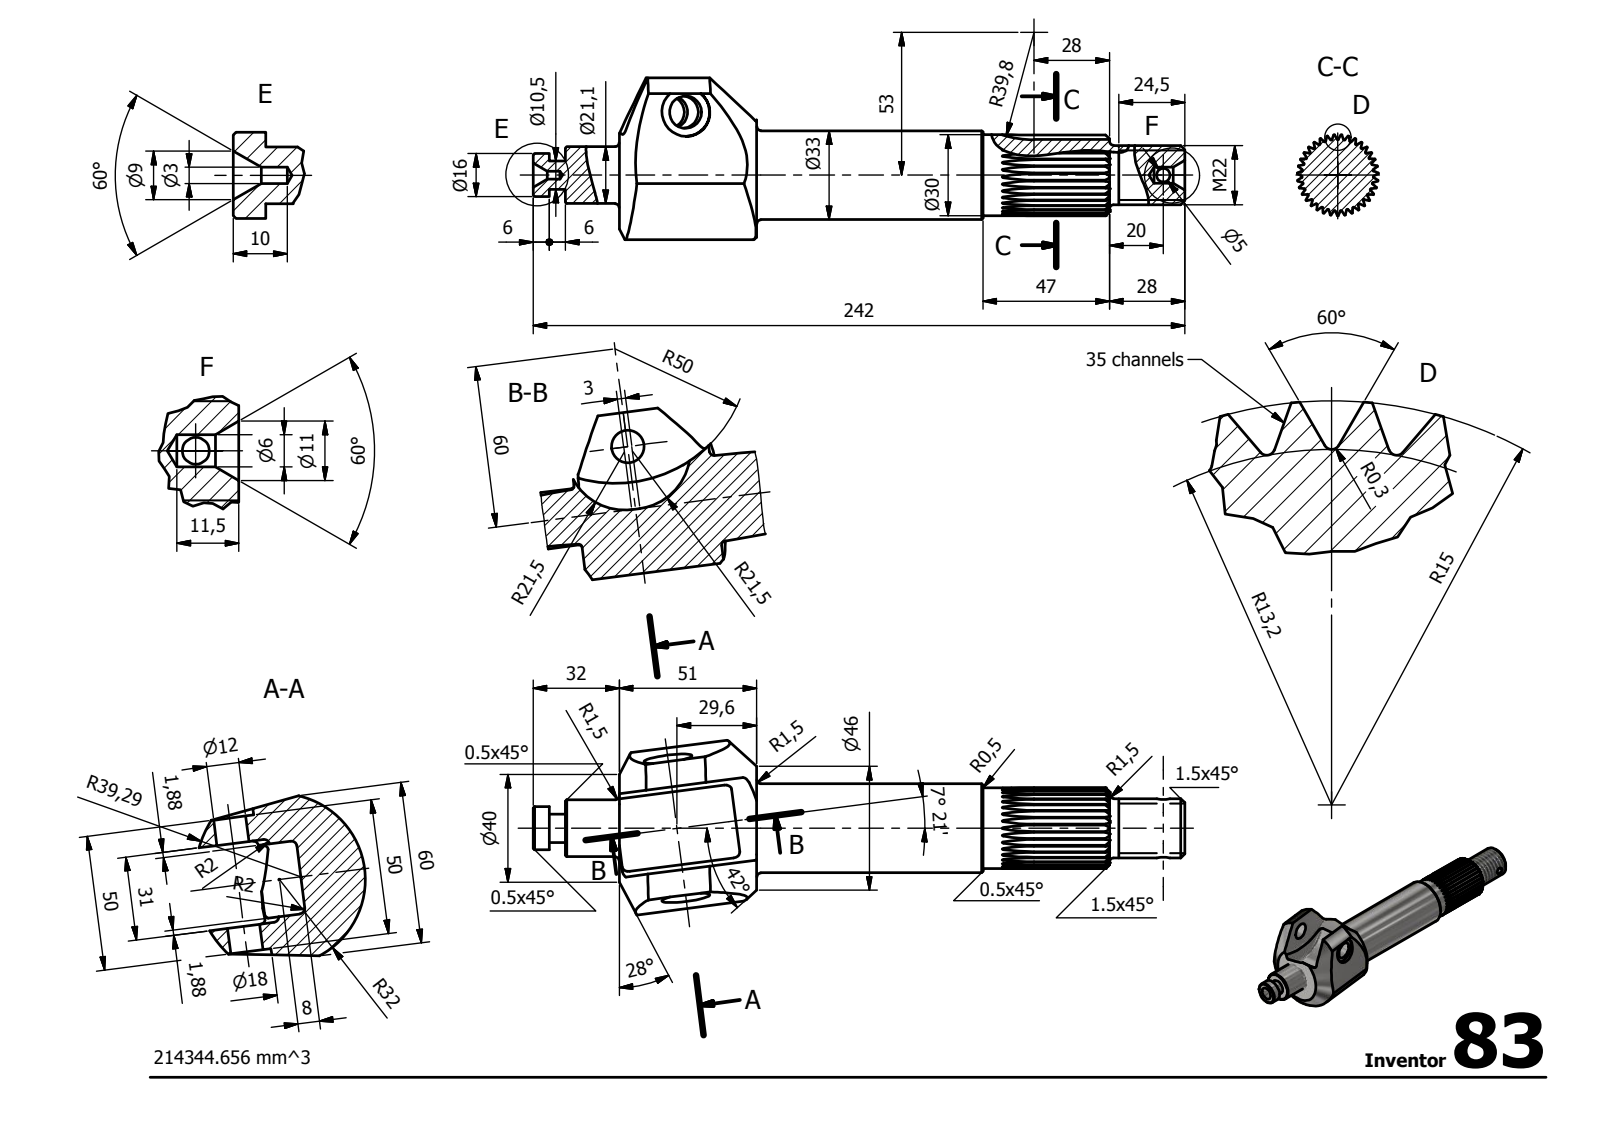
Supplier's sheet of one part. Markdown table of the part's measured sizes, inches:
| quantity | value |
| --- | --- |
| STEP written by | Autodesk Inventor 2014 (AUTOMOTIVE_DESIGN) |
| units | inches |
| bodies | 1 solid, 305 faces (87 planar, 58 cylindrical, 160 other) |
| overall size | 9.528 × 2.552 × 2.366 |
| volume | 13.08 in³ |
| surface area | 55.79 in² |
| round holes (diameter × count) | 0.118 × 1, 0.197 × 1, 0.236 × 1, 0.472 × 1 |
| round bosses / shafts (diameter × count) | 1.299 × 1, 1.181 × 1, 0.866 × 1, 0.831 × 1, 0.63 × 1, 0.413 × 1 |
| partial cylindrical surfaces (radius × count) | 0.012 × 35, 0.079 × 2, 0.354 × 2, 0.846 × 2, 1.26 × 1, 1.547 × 1, 1.969 × 1 |
| main face-to-face distances | 1.22, 2.008, 0.074, 1.146, 0.374, 0.448, 1.521, 1.595, 1.072, 0.787 |
